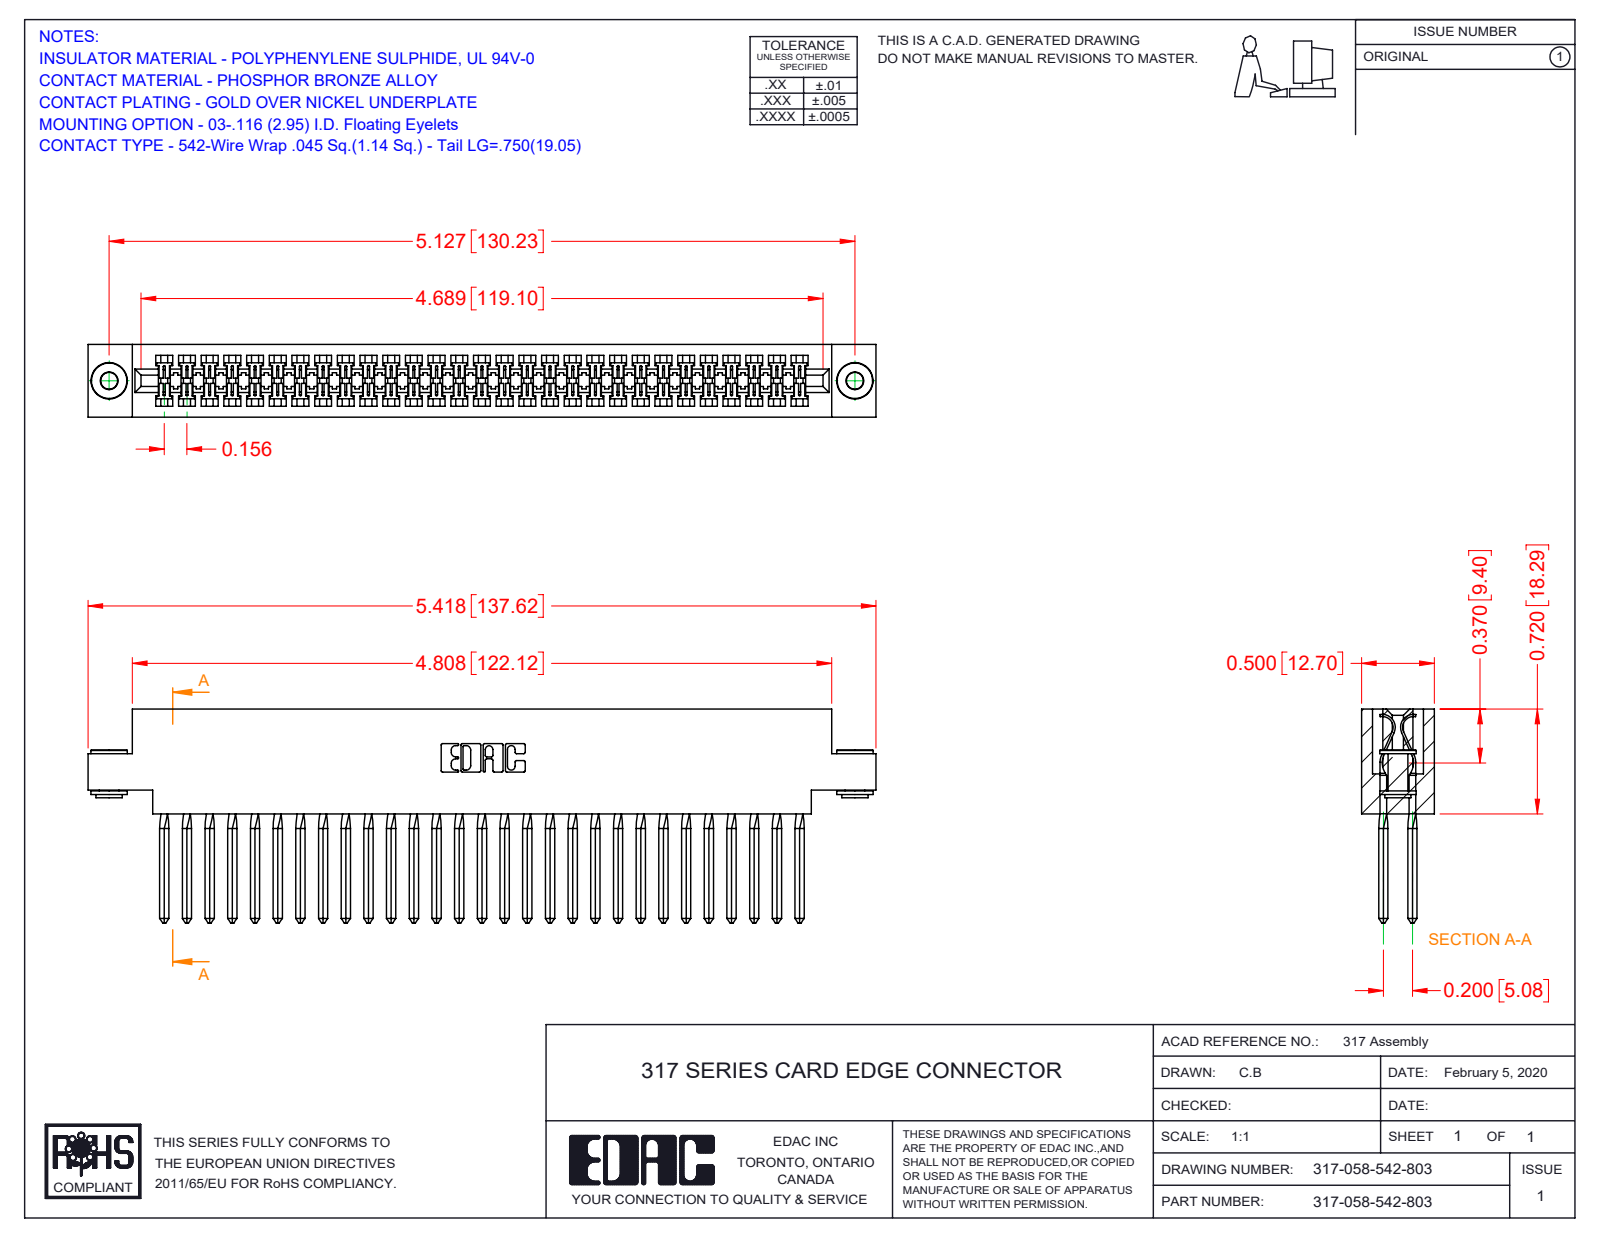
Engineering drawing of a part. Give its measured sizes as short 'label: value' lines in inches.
name: 317-290-003_542; 317-058-542-803; 317 Part_.156 Dia - TH; 345-250-002_345-250-002-102
written by: SolidWorks 2016 (CONFIG_CONTROL_DESIGN)
unit: in
bodies: 61 solids, 3446 faces (2736 planar, 470 cylindrical, 240 other)
size: 5.418 × 1.47 × 0.5
volume: 1.351 in³; area: 47.42 in²
holes: 2× ⌀0.116, 2× ⌀0.156
bosses: 2× ⌀0.25, 2× ⌀0.18, 2× ⌀0.136
rounds: 116× R0.006, 22× R0.01, 6× R0.007, 6× R0.031, 3× R0.026, 2× R0.074, 2× R0.089, 2× R0.1
face distances: 0.5, 0.075, 0.425, 0.35, 0.2, 0.11, 0.046, 0.116, 0.128, 0.372
hole spacings: 5.127
